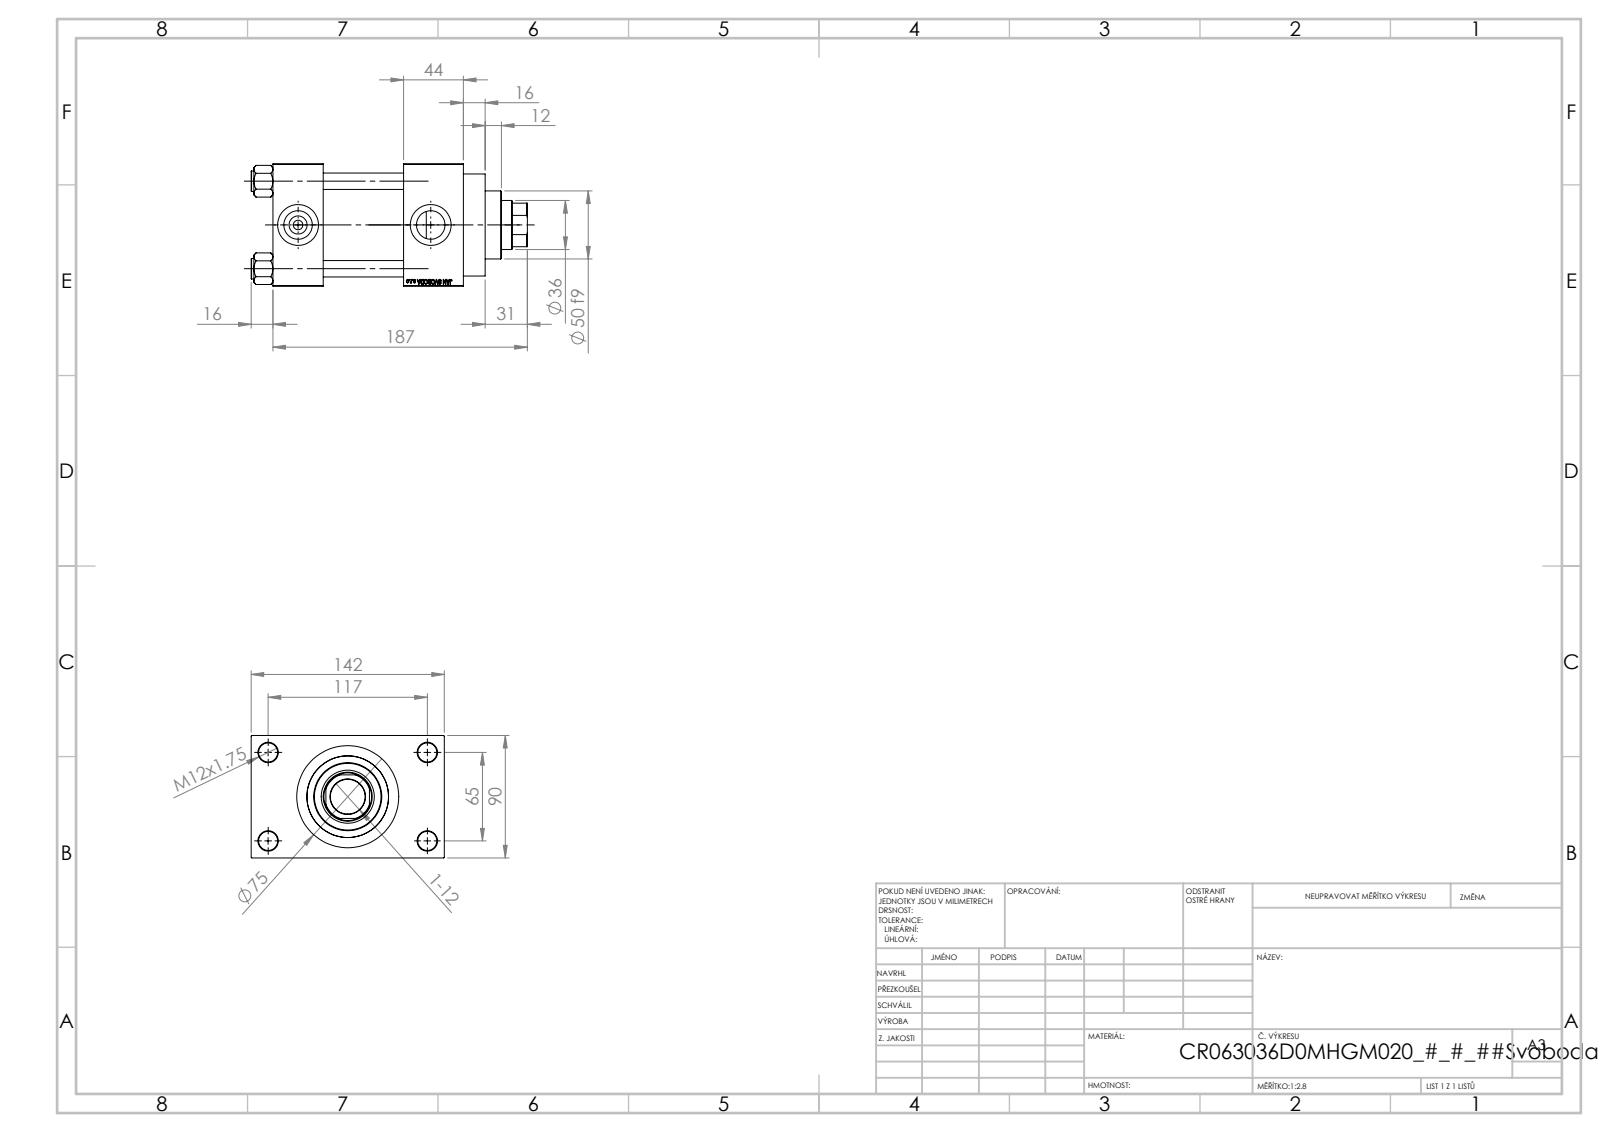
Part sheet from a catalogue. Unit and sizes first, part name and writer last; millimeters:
Units: millimetres
Overall size (bounding box): 203 × 142 × 90
Round holes (diameter × count): ⌀12 ×4, ⌀14 ×4, ⌀7 ×2, ⌀20.96 ×2, ⌀30 ×2, ⌀25.5 ×1, ⌀36 ×1, ⌀39 ×1, ⌀50 ×1, ⌀60 ×1, ⌀63 ×1
Round bosses / shafts (diameter × count): ⌀15 ×4, ⌀75 ×1, ⌀69 ×1
Partial cylindrical surfaces — rounded edges, fillets, slot ends (radius × count): R17.5 ×1
Main face-to-face distances: 90, 59, 37, 96, 140, 103, 44, 26, 116, 142
Hole centre spacings: 26.35, 45.47, 64.3, 66.92, 69.81, 90.65, 111.34, 65
Volume: 1 112 000 mm³ · Surface area: 205 784 mm²
Bodies: 11 solids, 1103 faces (497 planar, 88 cylindrical, 518 other)
Part name (STEP PRODUCT): V215CR_D_Body; V215_VC_A; V215CR_VCP_D; V215CR_D_TYCINKA (+1 more)
STEP written by: SolidWorks 2019 (CONFIG_CONTROL_DESIGN)
